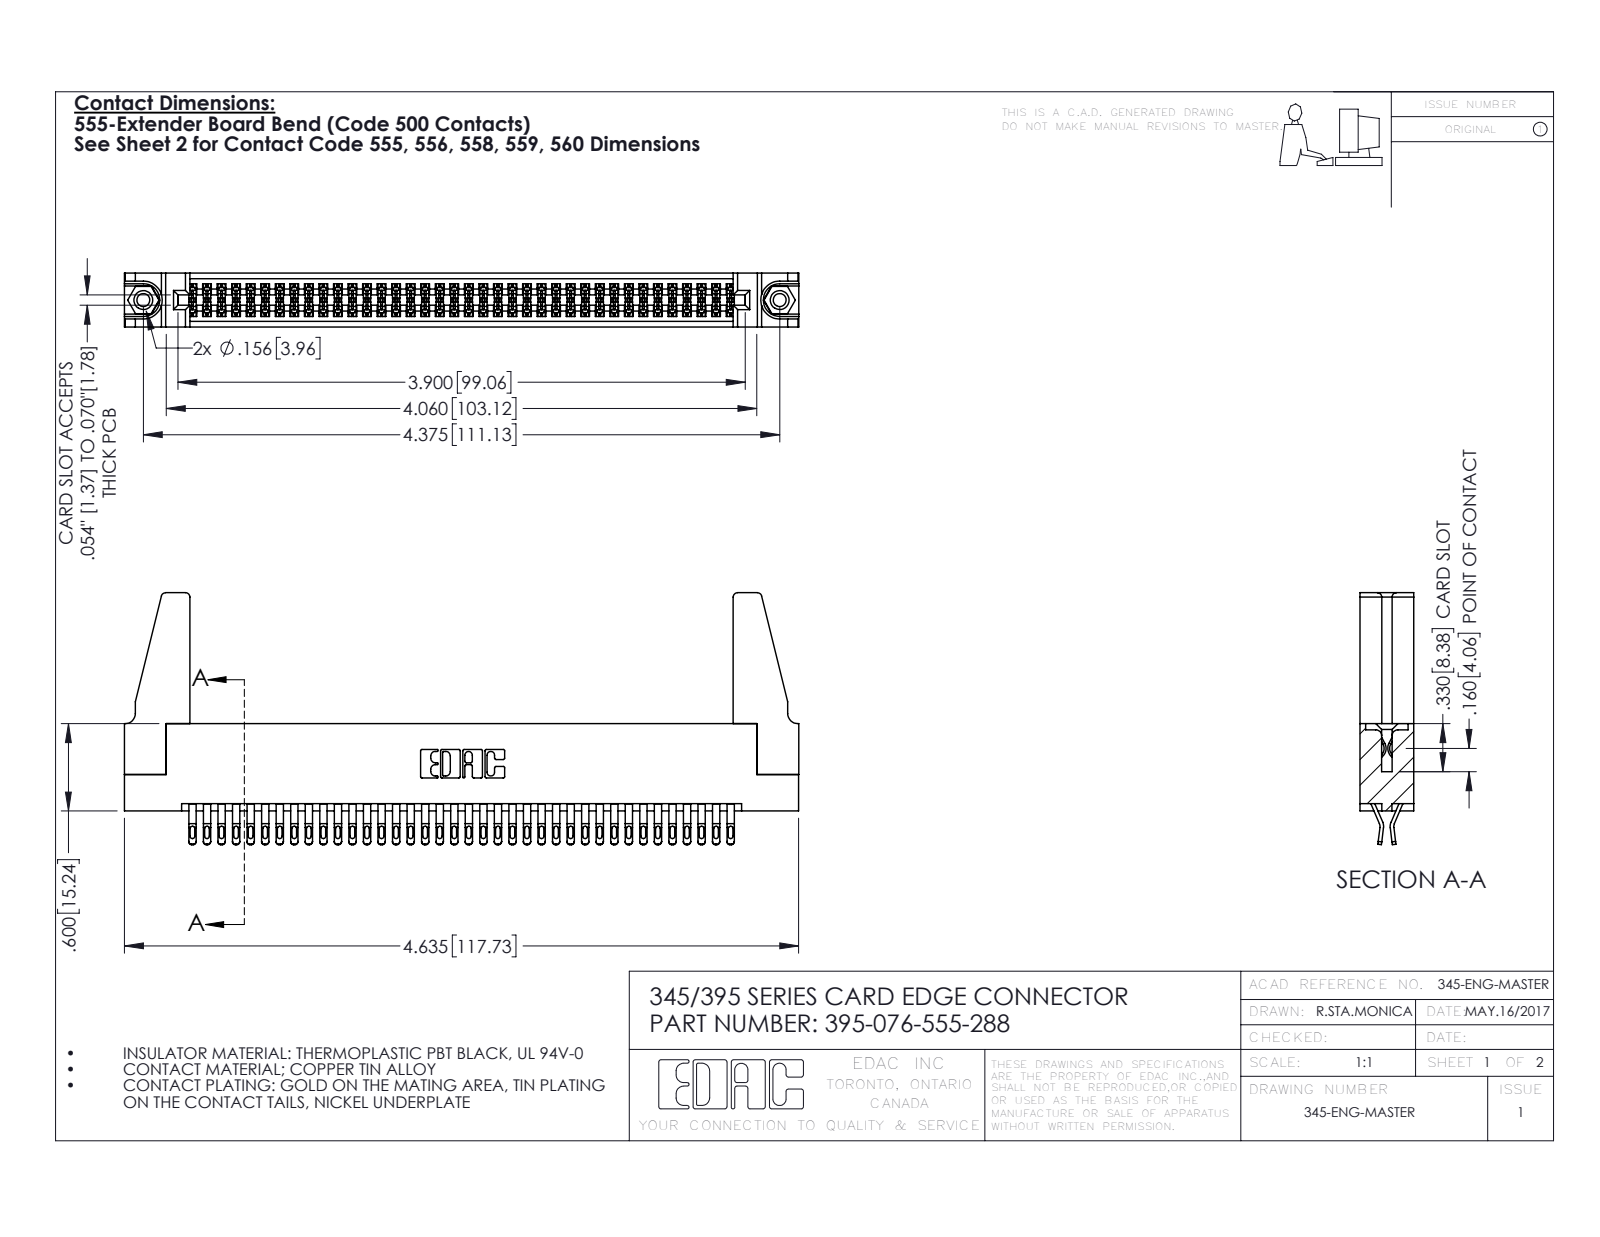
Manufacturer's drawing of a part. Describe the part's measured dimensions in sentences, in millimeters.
The part is named "345 Part_Flush Mounting Lugs - 0.156 Dia-TH; 345-292-001_555 Tail; 345-250-001_345-250-001-102; 345-220-078_345-220-088 (+1 more)". Its 3-D file was written by "SolidWorks 2016 (CONFIG_CONTROL_DESIGN)". It is 81 solids with 4506 faces: 2508 planar, 1982 cylindrical and 16 other. Overall it measures 117.8 by 44 by 9.4 millimeters. Its volume is 14 900 cubic millimeters and its surface area 20 990 square millimeters. Round holes: 2 of diameter 2.3, 2 of diameter 3.2, 2 of diameter 4, 1 of diameter 1.6. Round bosses or shafts: 2 of diameter 3.9. Partial cylindrical surfaces (rounded edges, fillets, slot ends): 190 of radius 0.4, 152 of radius 0.5, 114 of radius 0.2, 22 of radius 0.3, 8 of radius 0.8, 6 of radius 0.2, 6 of radius 0.8, 3 of radius 0.7. The main face-to-face distances are 1.8, 7.6, 9.4, 5.1, 0.6, 2.5, 6.9, 5.7, 4.4, 3.8. The hole center spacings are 6.9, 105.1, 111.1.
